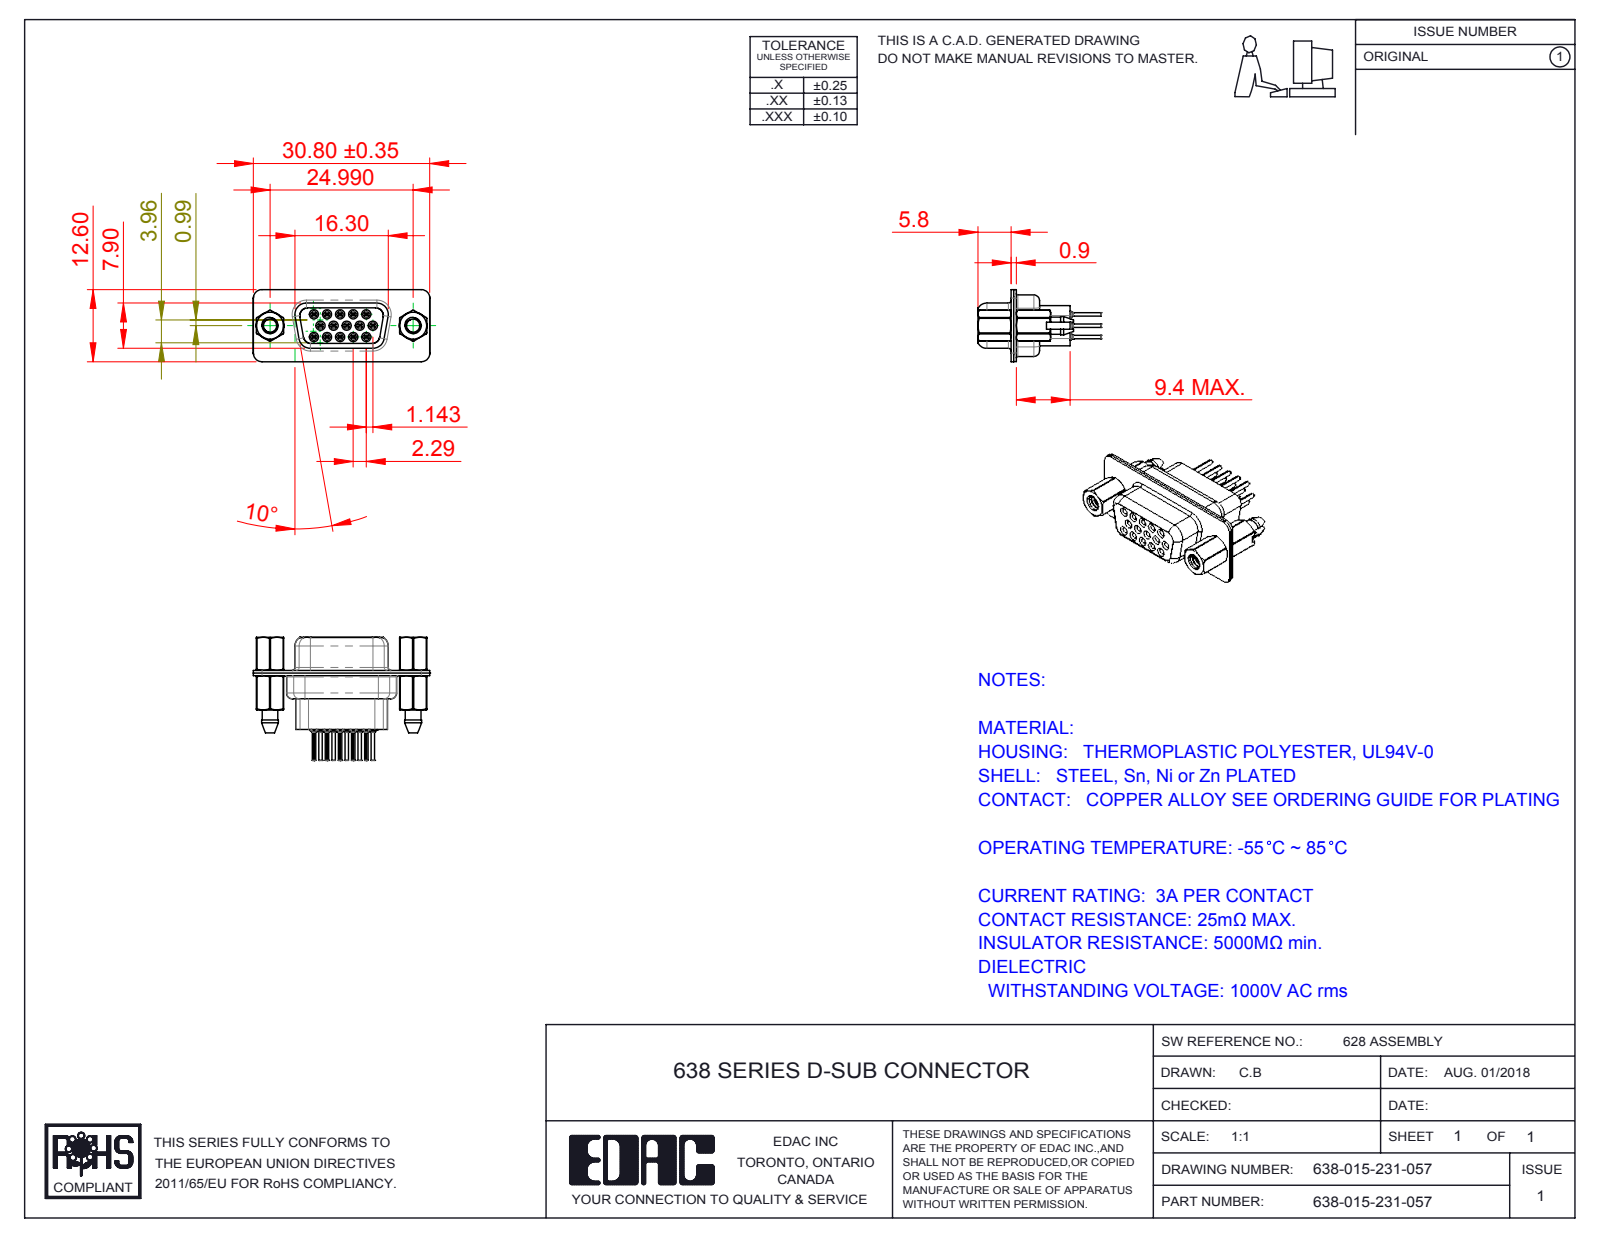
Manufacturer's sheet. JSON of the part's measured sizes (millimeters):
{"part_name": "638-015-231-057; 638 Housing_15 Contacts HP; 638 Contact Row 1_31H; 638 Contact Row 2_31H (+5 more)", "step_written_by": "SolidWorks 2016 (CONFIG_CONTROL_DESIGN)", "units": "millimeters", "bodies": {"solids": 22, "faces": 2324, "planar": 586, "cylindrical": 736, "other": 1002}, "overall_size": [30.81, 21.5, 12.6], "volume_mm3": 2208, "surface_area_mm2": 7299, "round_holes": [[0.2, 15], [0.8, 15], [1, 15], [1.1, 15], [1.6, 15], [1.7, 15], [1.8, 15], [2, 2], [2.26, 2], [2.29, 2], [4, 2], [4.05, 2]], "round_bosses_or_shafts": [[2, 15], [1.5, 15], [1.2, 15], [0.6, 15], [4.95, 2], [4.8, 2], [2.79, 2]], "partial_cylinders_radius": [[0.1, 30], [1.5, 22], [2, 12], [0.28, 10], [1.55, 8], [1.35, 5], [0.25, 4], [0.5, 4]], "face_to_face_distances": [0.45, 0.9, 0.4, 1.43, 6.6, 8.88, 4.76, 7, 5.8, 2.28], "hole_center_spacings": [3.96, 2.28, 4.57, 2.29, 6.05, 6.04, 6.86, 7.92]}
